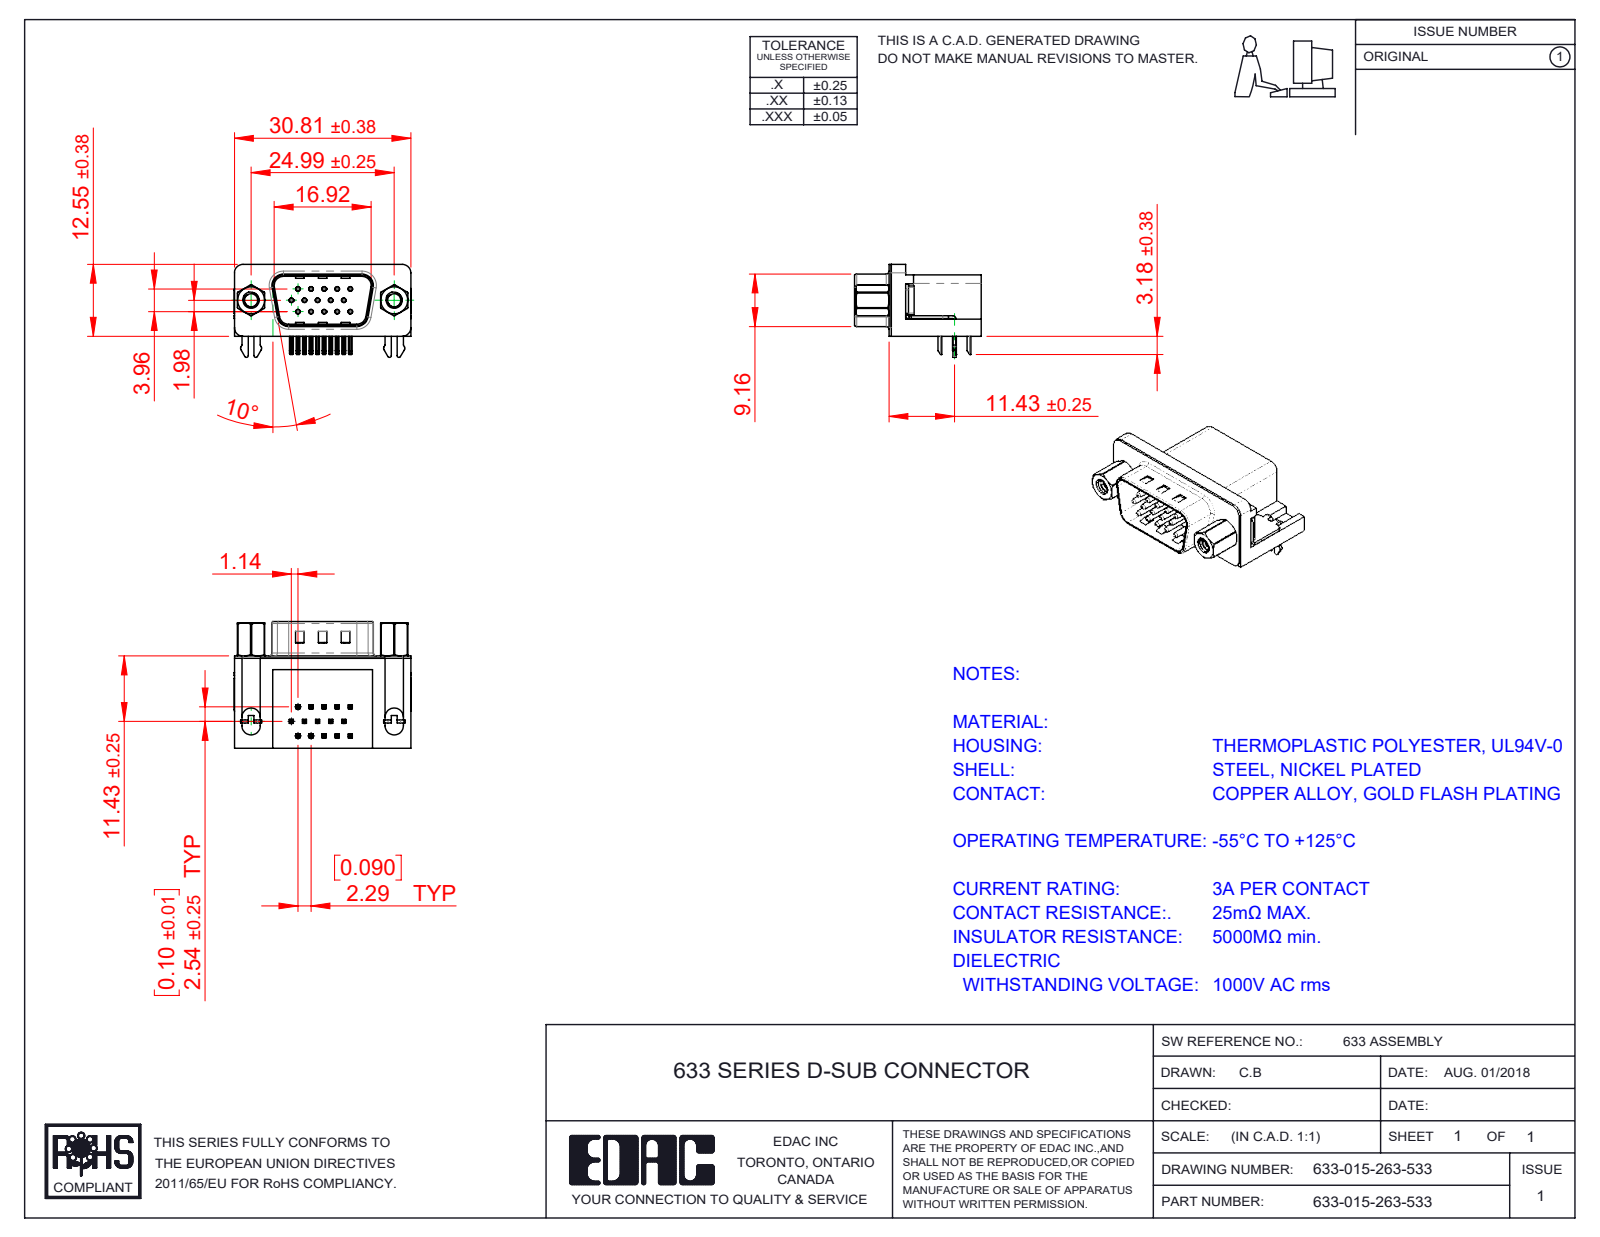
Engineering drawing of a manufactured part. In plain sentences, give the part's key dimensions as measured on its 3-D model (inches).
The part is named "633 Housing_15 Contact; 633 4-40 Hex Standoff; 633 4-40 Threaded Rivet; 633 2 Prong Board Lock (+5 more)". Its 3-D file was written by "SolidWorks 2016 (CONFIG_CONTROL_DESIGN)". It is 23 solids with 1603 faces: 915 planar, 515 cylindrical and 173 other. Overall it measures 1.216 by 0.87 by 0.64 inches. Its volume is 0.261 cubic inches and its surface area 9.119 square inches. Round holes: 15 of diameter 0.014, 15 of diameter 0.031, 2 of diameter 0.089, 2 of diameter 0.09, 2 of diameter 0.157, 2 of diameter 0.189, 2 of diameter 0.197. Round bosses or shafts: 15 of diameter 0.03, 2 of diameter 0.193, 2 of diameter 0.187, 2 of diameter 0.154, 2 of diameter 0.11. Partial cylindrical surfaces (rounded edges, fillets, slot ends): 68 of radius 0.01, 30 of radius 0.005, 16 of radius 0.039, 14 of radius 0.02, 8 of radius 0.063, 7 of radius 0.059, 4 of radius 0.013, 4 of radius 0.035. The main face-to-face distances are 0.016, 0.407, 0.618, 0.634, 0.114, 0.02, 0.098, 0.264, 0.014, 0.421. The hole center spacings are 0.156, 0.09, 0.18, 0.09, 0.238, 0.27, 0.312, 0.238.
